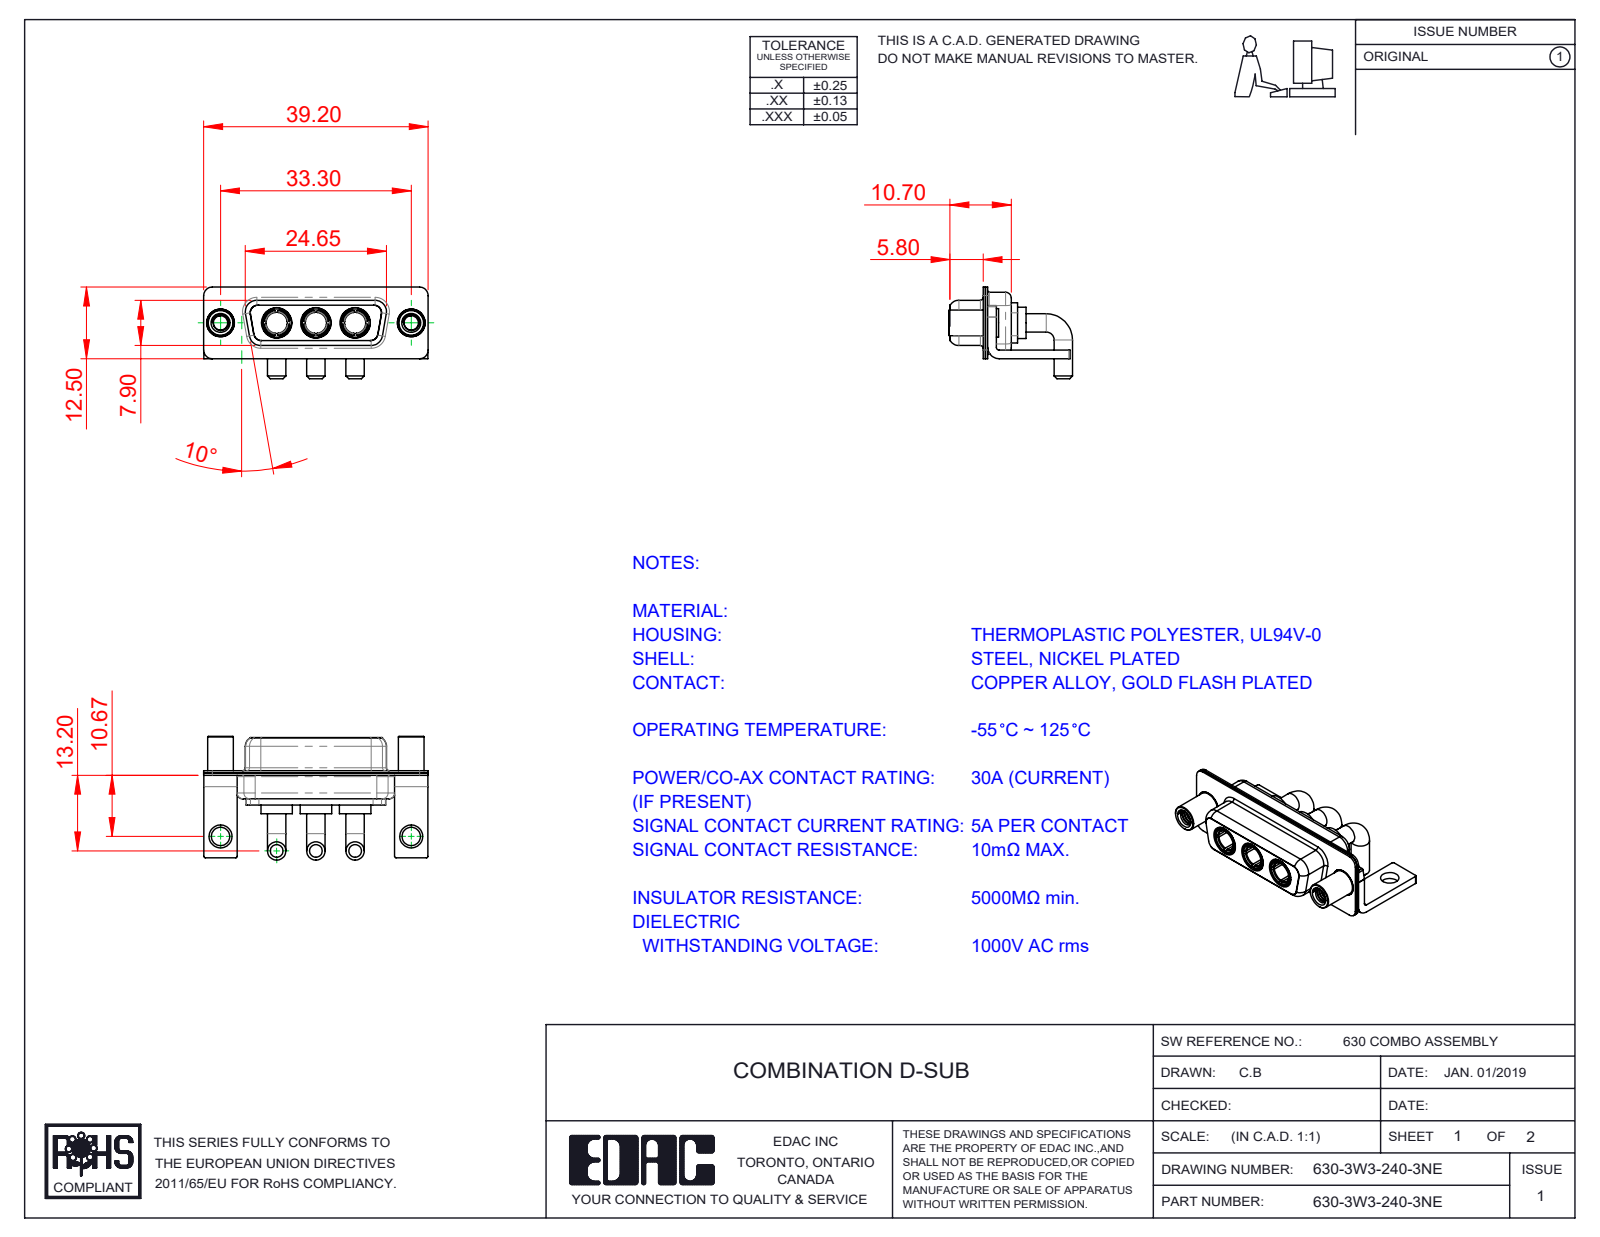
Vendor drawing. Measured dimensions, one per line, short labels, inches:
name: Power Socket_30A RA; 630Combo Threaded Standoff_D; 630Combo Shell Front_15 Contacts; 630Combo Shell Rear_15 Contacts (+3 more)
written by: SolidWorks 2020 (CONFIG_CONTROL_DESIGN)
unit: in
bodies: 13 solids, 611 faces (176 planar, 284 cylindrical, 151 other)
size: 1.543 × 0.85 × 0.63
volume: 0.19 in³; area: 10.7 in²
holes: 5× ⌀0.191, 3× ⌀0.146, 3× ⌀0.209, 2× ⌀0.098, 2× ⌀0.126, 2× ⌀0.157, 2× ⌀0.159
bosses: 6× ⌀0.126, 3× ⌀0.217, 3× ⌀0.205, 3× ⌀0.195, 3× ⌀0.187, 3× ⌀0.148, 2× ⌀0.197, 2× ⌀0.195
rounds: 16× R0.01, 16× R0.059, 13× R0.079, 12× R0.053, 8× R0.063, 5× R0.02, 4× R0.024, 4× R0.026
face distances: 0.016, 0.031, 0.055, 0.018, 0.059, 0.333, 0.071, 0.35, 0.278, 0.205
hole spacings: 0.27, 0.386, 0.656, 0.925, 1.311, 0.539
